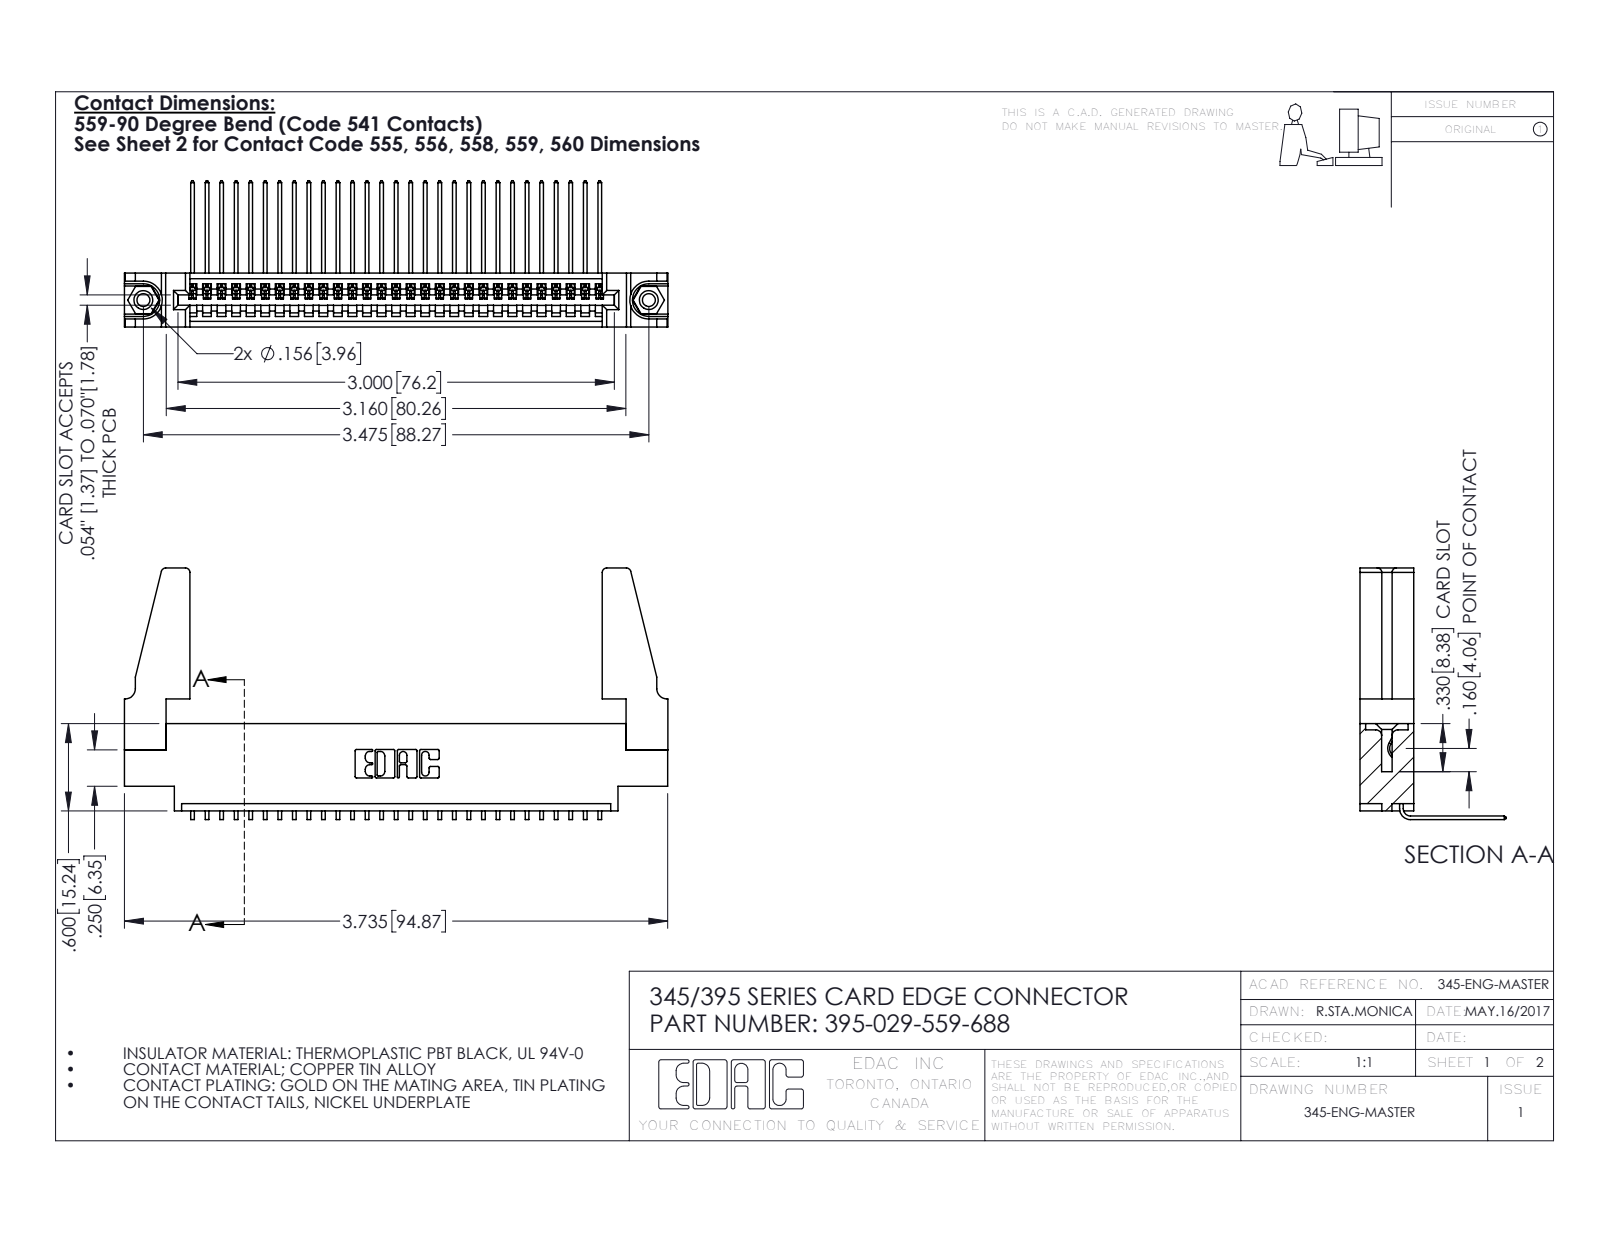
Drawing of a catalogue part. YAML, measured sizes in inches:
part_name: "395-029-559-688; 345-220-078_345-220-088; 345-250-001_345-250-001-102; 345-292-001_558 559 Tail - 1 (+1 more)"
step_written_by: "SolidWorks 2016 (CONFIG_CONTROL_DESIGN)"
units: inches
bodies: {solids: 34, faces: 1994, planar: 1374, cylindrical: 604, other: 16}
overall_size: [3.736, 1.729, 1.005]
volume: 0.741
surface_area: 23.96
round_holes:
  - {diameter: 0.089, count: 2}
  - {diameter: 0.125, count: 2}
  - {diameter: 0.156, count: 2}
  - {diameter: 0.064, count: 1}
round_bosses_or_shafts:
  - {diameter: 0.155, count: 2}
partial_cylinders:
  - {radius: 0.006, count: 58}
  - {radius: 0.01, count: 22}
  - {radius: 0.03, count: 8}
  - {radius: 0.007, count: 6}
  - {radius: 0.031, count: 6}
  - {radius: 0.026, count: 3}
  - {radius: 0.031, count: 2}
  - {radius: 0.04, count: 2}
face_to_face_distances: [0.37, 0.072, 0.298, 0.2, 0.098, 0.272, 0.025, 0.225, 0.175, 0.149]
hole_center_spacings: [0.27, 3.24, 3.475]
